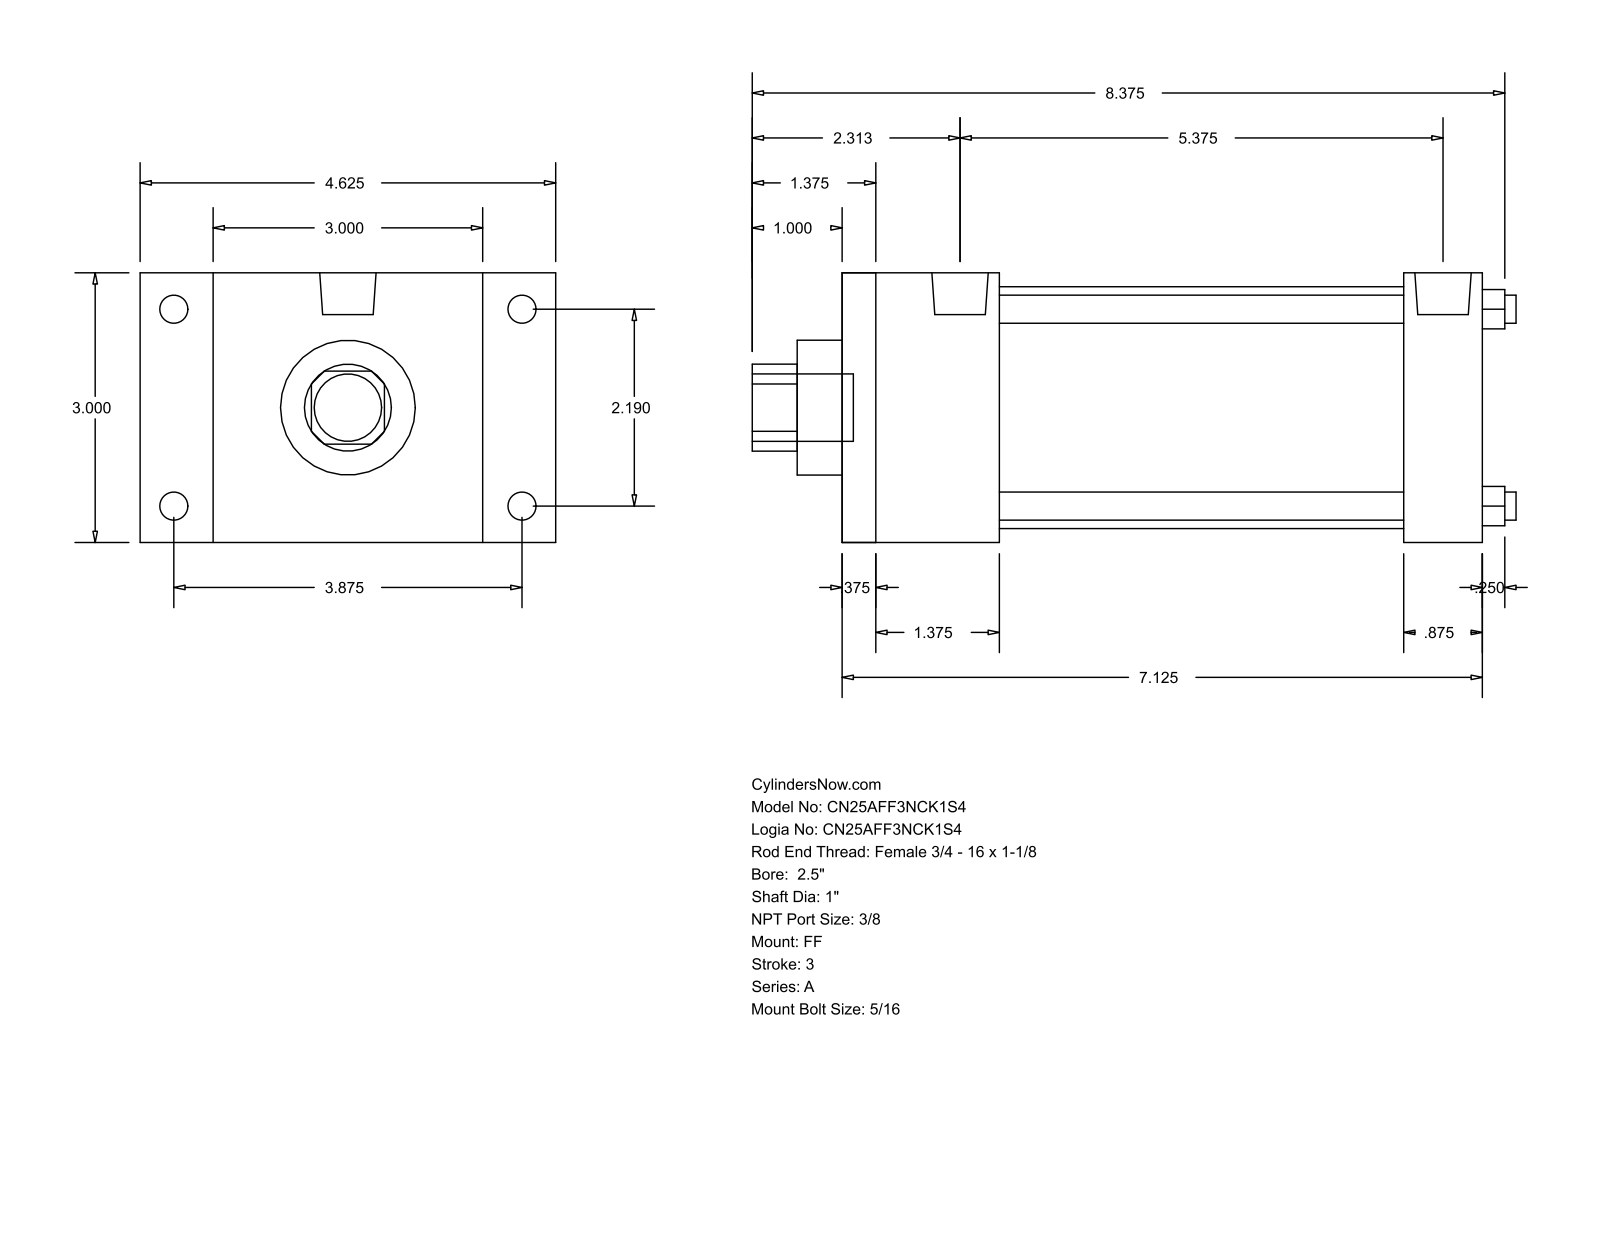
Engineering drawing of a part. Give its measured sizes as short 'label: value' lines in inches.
name: A_FF__0250_1
written by: GSSL Pune (CONFIG_CONTROL_DESIGN)
unit: in
bodies: 0 solids, 92 faces (64 planar, 28 cylindrical, 0 other)
size: 8.5 × 4.625 × 3
holes: 4× ⌀0.313, 1× ⌀1, 1× ⌀1.5, 1× ⌀2.69
bosses: 4× ⌀0.313, 4× ⌀0.219, 2× ⌀0.627, 1× ⌀0.75
rounds: 1× R0.484
face distances: 3, 7.125, 0.375, 6.75, 1.75, 6.25, 1.375, 5.875, 4.5, 5.375
hole spacings: 1.548, 2.19, 3.097
